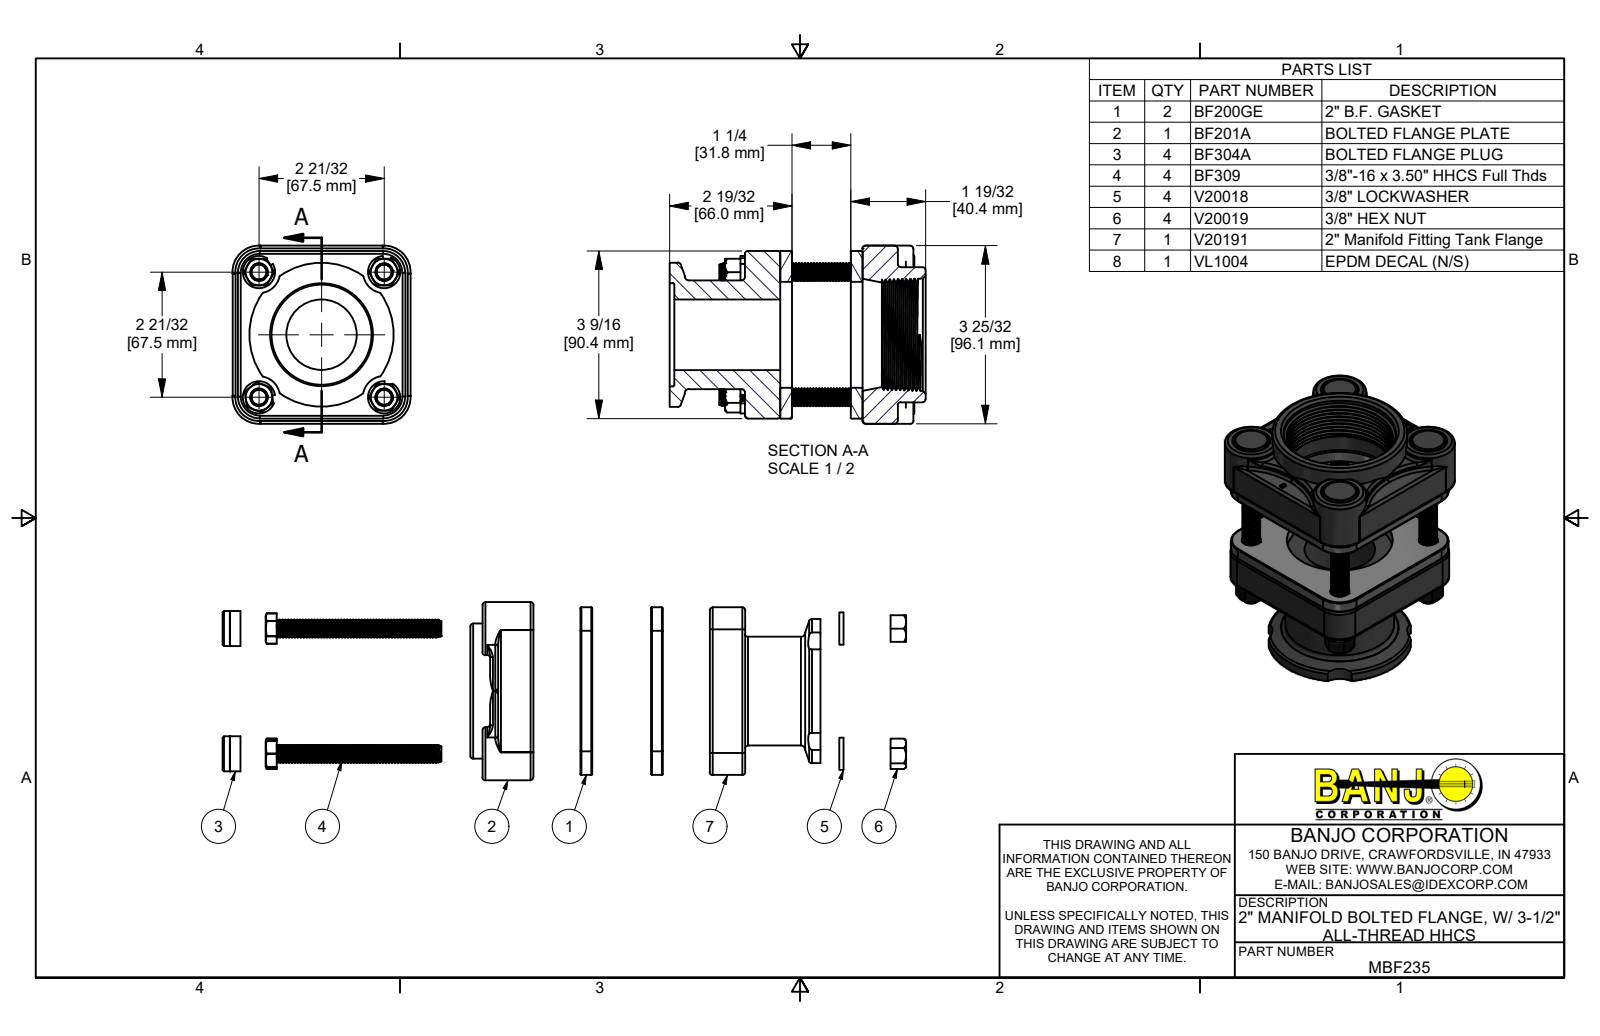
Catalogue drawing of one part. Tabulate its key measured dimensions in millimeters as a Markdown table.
| quantity | value |
| --- | --- |
| part name | MBF235; BF201A; V20191; V20018 (+4 more) |
| STEP written by | Autodesk Inventor 2019 (AUTOMOTIVE_DESIGN) |
| units | millimeters |
| bodies | 20 solids, 1747 faces (306 planar, 674 cylindrical, 767 other) |
| overall size | 138.2 × 96.1 × 96.1 |
| volume | 452 800 mm³ |
| surface area | 133 500 mm² |
| round holes (diameter × count) | 7.8 × 4, 9.7 × 4, 9.8 × 4, 10.3 × 4, 10.4 × 4, 18.2 × 4, 19.1 × 4, 38.1 × 1, 55.6 × 1, 57.2 × 1 |
| round bosses / shafts (diameter × count) | 8.2 × 220, 28.6 × 4, 18.8 × 4, 17.4 × 4, 9.5 × 4, 72.9 × 1, 58.7 × 1 |
| partial cylindrical surfaces (radius × count) | 1.5 × 24, 0.5 × 16, 4.1 × 8, 8.2 × 4, 11.4 × 4, 11.9 × 4, 12.7 × 4, 40.6 × 4 |
| main face-to-face distances | 38.1, 44.5, 6.4, 57.2, 63.5, 19.1, 25.4, 31.8, 2.8, 93.2 |
| hole center spacings | 47.8, 67.5, 95.5 |
